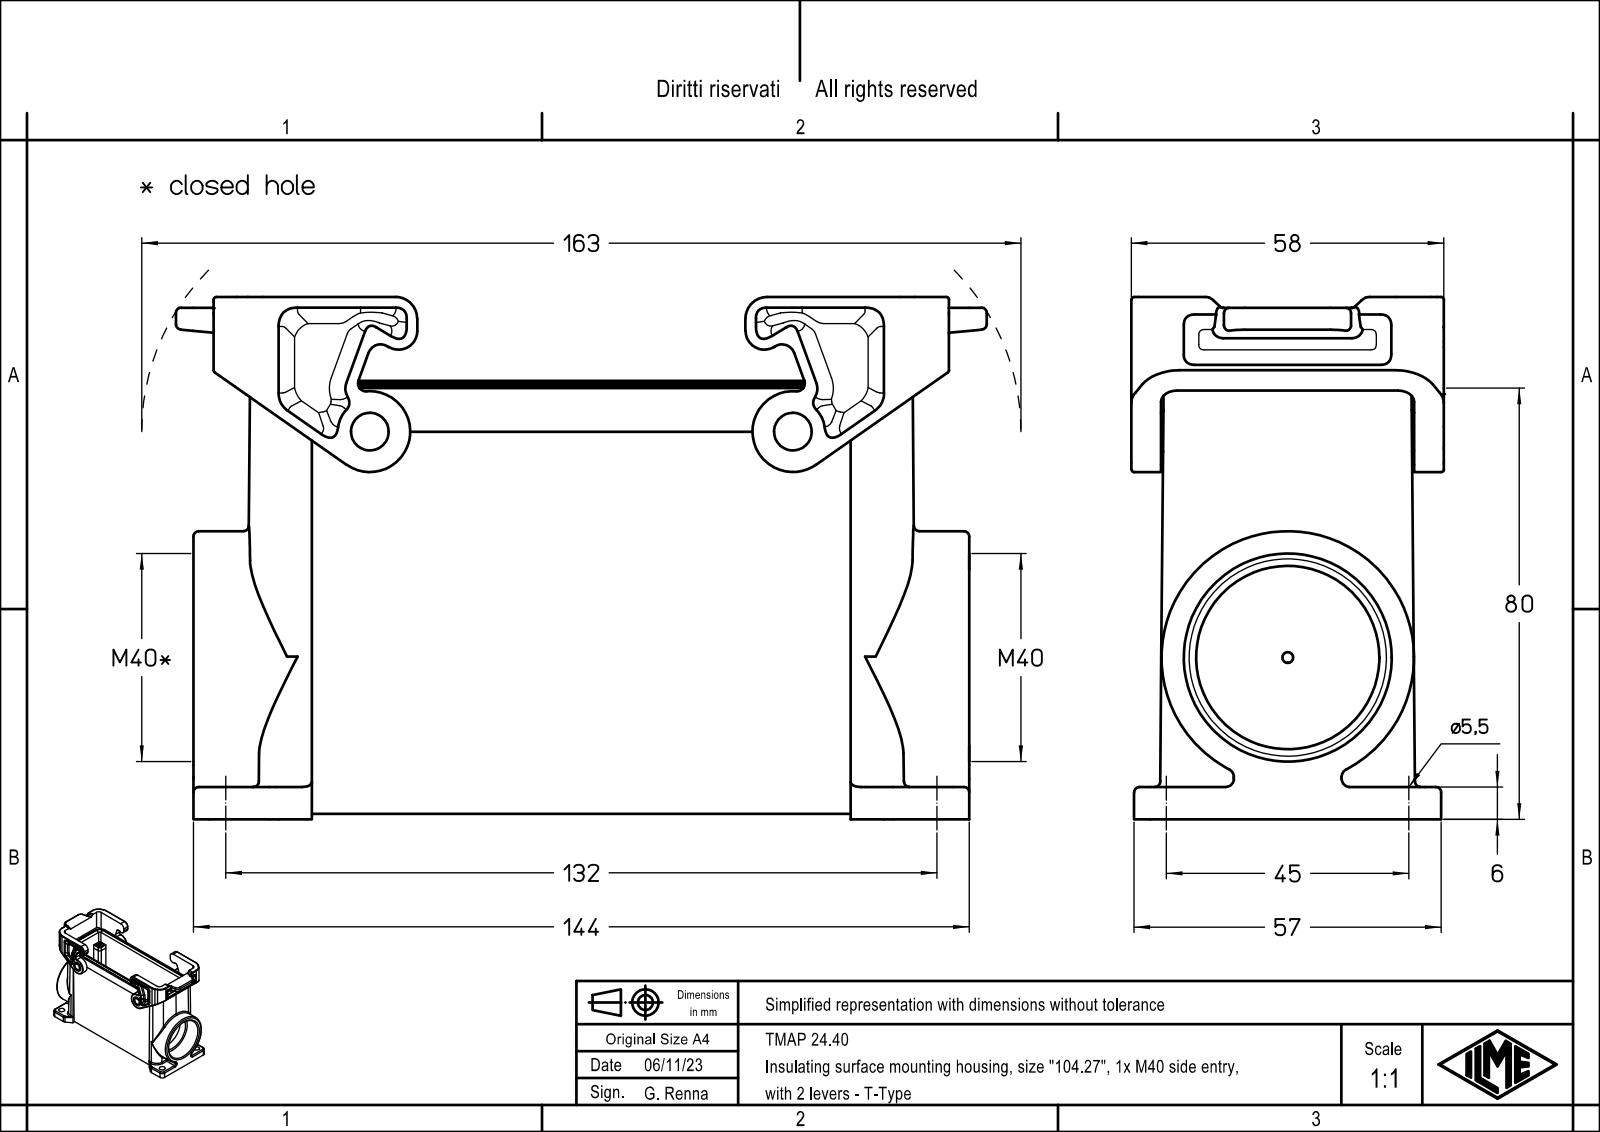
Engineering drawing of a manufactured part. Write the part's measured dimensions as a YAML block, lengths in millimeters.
part_name: "TMAP 24.40"
step_written_by: "Creo Elements/Direct Modeling 20.1B 02-Apr-2019 (C) Parametric Technology GmbH (AUTOMOTIVE_DESIGN)"
units: millimeters
bodies: {solids: 1, faces: 414, planar: 204, cylindrical: 158, other: 52}
overall_size: [150.5, 96.9, 58]
volume: 210336
surface_area: 80998
round_holes:
  - {diameter: 5.5, count: 4}
  - {diameter: 34, count: 1}
  - {diameter: 38.6, count: 1}
round_bosses_or_shafts:
  - {diameter: 7, count: 2}
  - {diameter: 46.87, count: 1}
partial_cylinders:
  - {radius: 3, count: 20}
  - {radius: 1, count: 16}
  - {radius: 2, count: 16}
  - {radius: 1.5, count: 10}
  - {radius: 1.3, count: 8}
  - {radius: 6, count: 8}
  - {radius: 7, count: 8}
  - {radius: 4, count: 6}
face_to_face_distances: [35.2, 5.5, 5.9, 41.1, 1, 6.5, 11.4, 46.6, 52.5, 5]
hole_center_spacings: [45, 132, 139.46]
